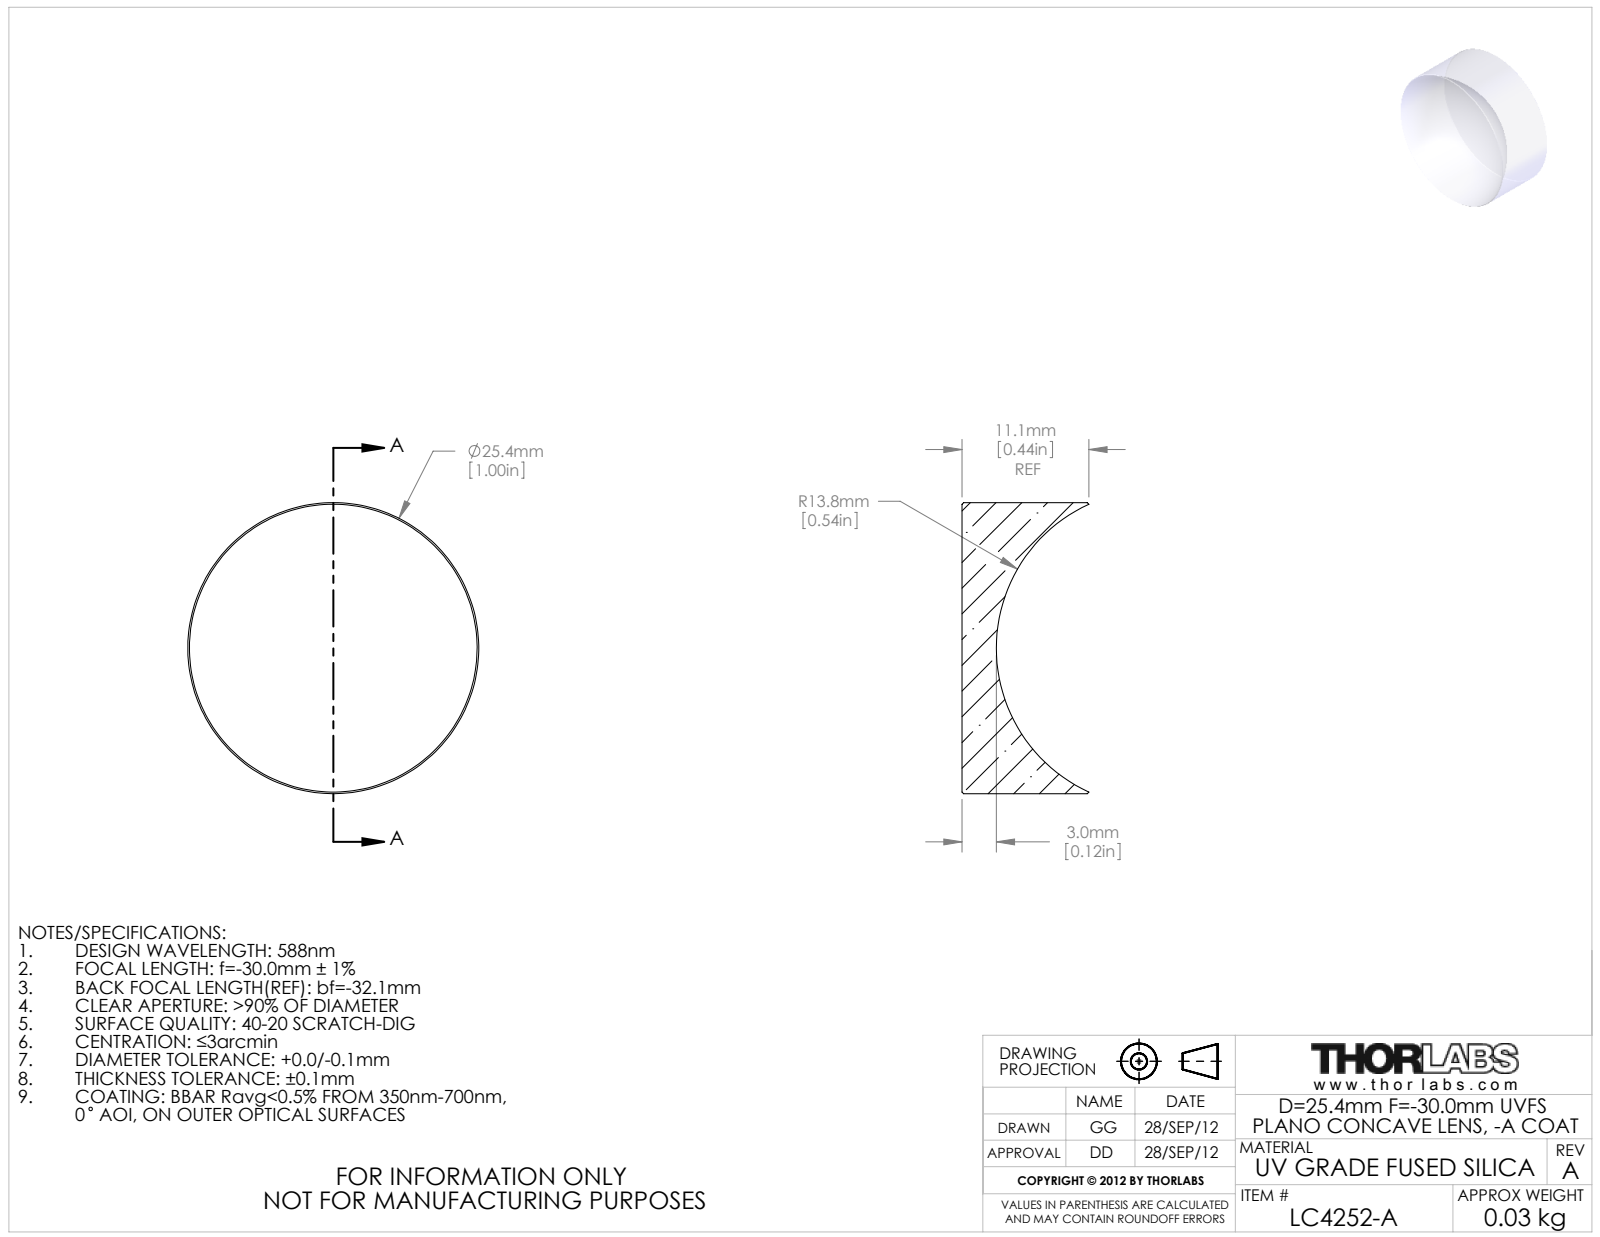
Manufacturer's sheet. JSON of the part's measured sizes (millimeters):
{"part_name": "25023-E0W", "step_written_by": "SolidWorks 2011 (CONFIG_CONTROL_DESIGN)", "units": "millimeters", "bodies": {"solids": 1, "faces": 9, "planar": 1, "cylindrical": 2, "other": 6}, "overall_size": [25.4, 25.4, 11.08], "volume_mm3": 3335, "surface_area_mm2": 2089, "round_bosses_or_shafts": [[25.4, 1]]}
